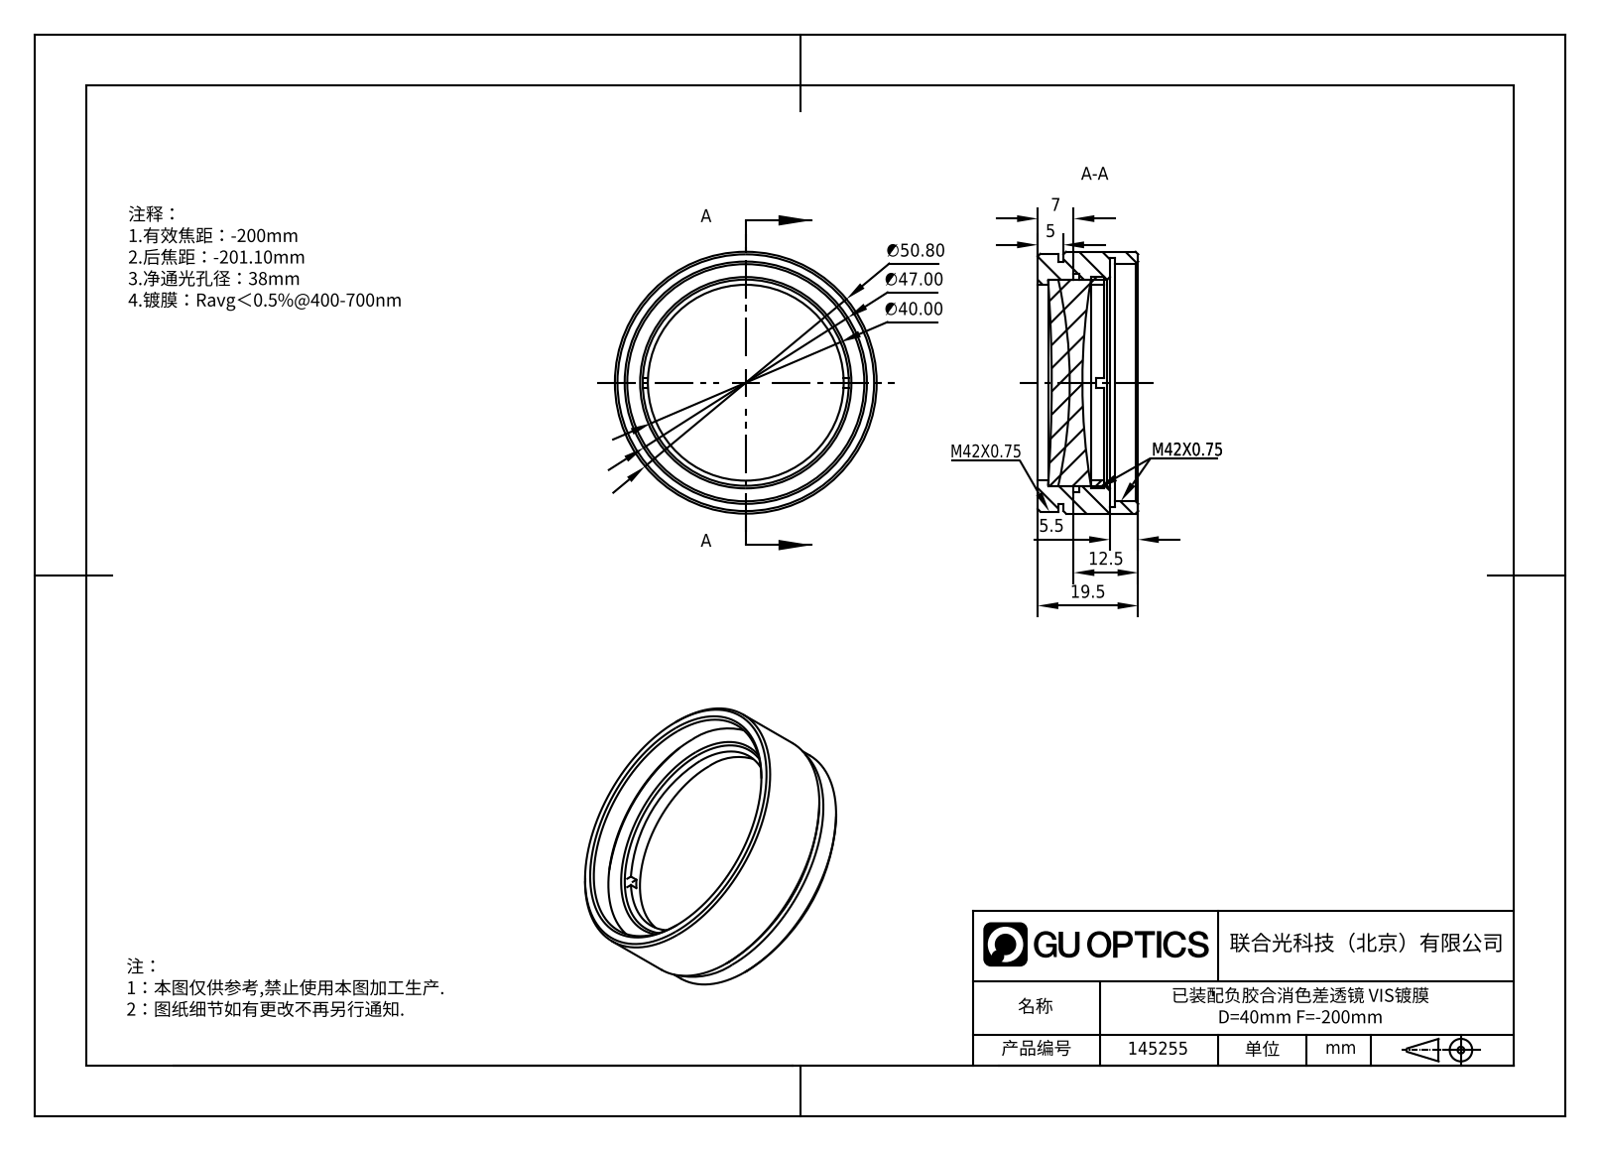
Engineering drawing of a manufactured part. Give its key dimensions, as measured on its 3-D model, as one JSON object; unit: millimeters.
{"part_name": "145255", "step_written_by": "SolidWorks 2020 (CONFIG_CONTROL_DESIGN)", "units": "millimeters", "bodies": {"solids": 4, "faces": 62, "planar": 18, "cylindrical": 26, "other": 18}, "overall_size": [50.8, 50.8, 19.5], "volume_mm3": 21509, "surface_area_mm2": 15414, "round_holes": [[38, 1], [40, 1], [42.3, 1], [46, 1], [48.3, 1]], "round_bosses_or_shafts": [[50.8, 1], [50, 1], [47, 1], [41, 1]], "face_to_face_distances": [1, 14, 7, 3, 10, 2, 4, 5, 8, 6]}
